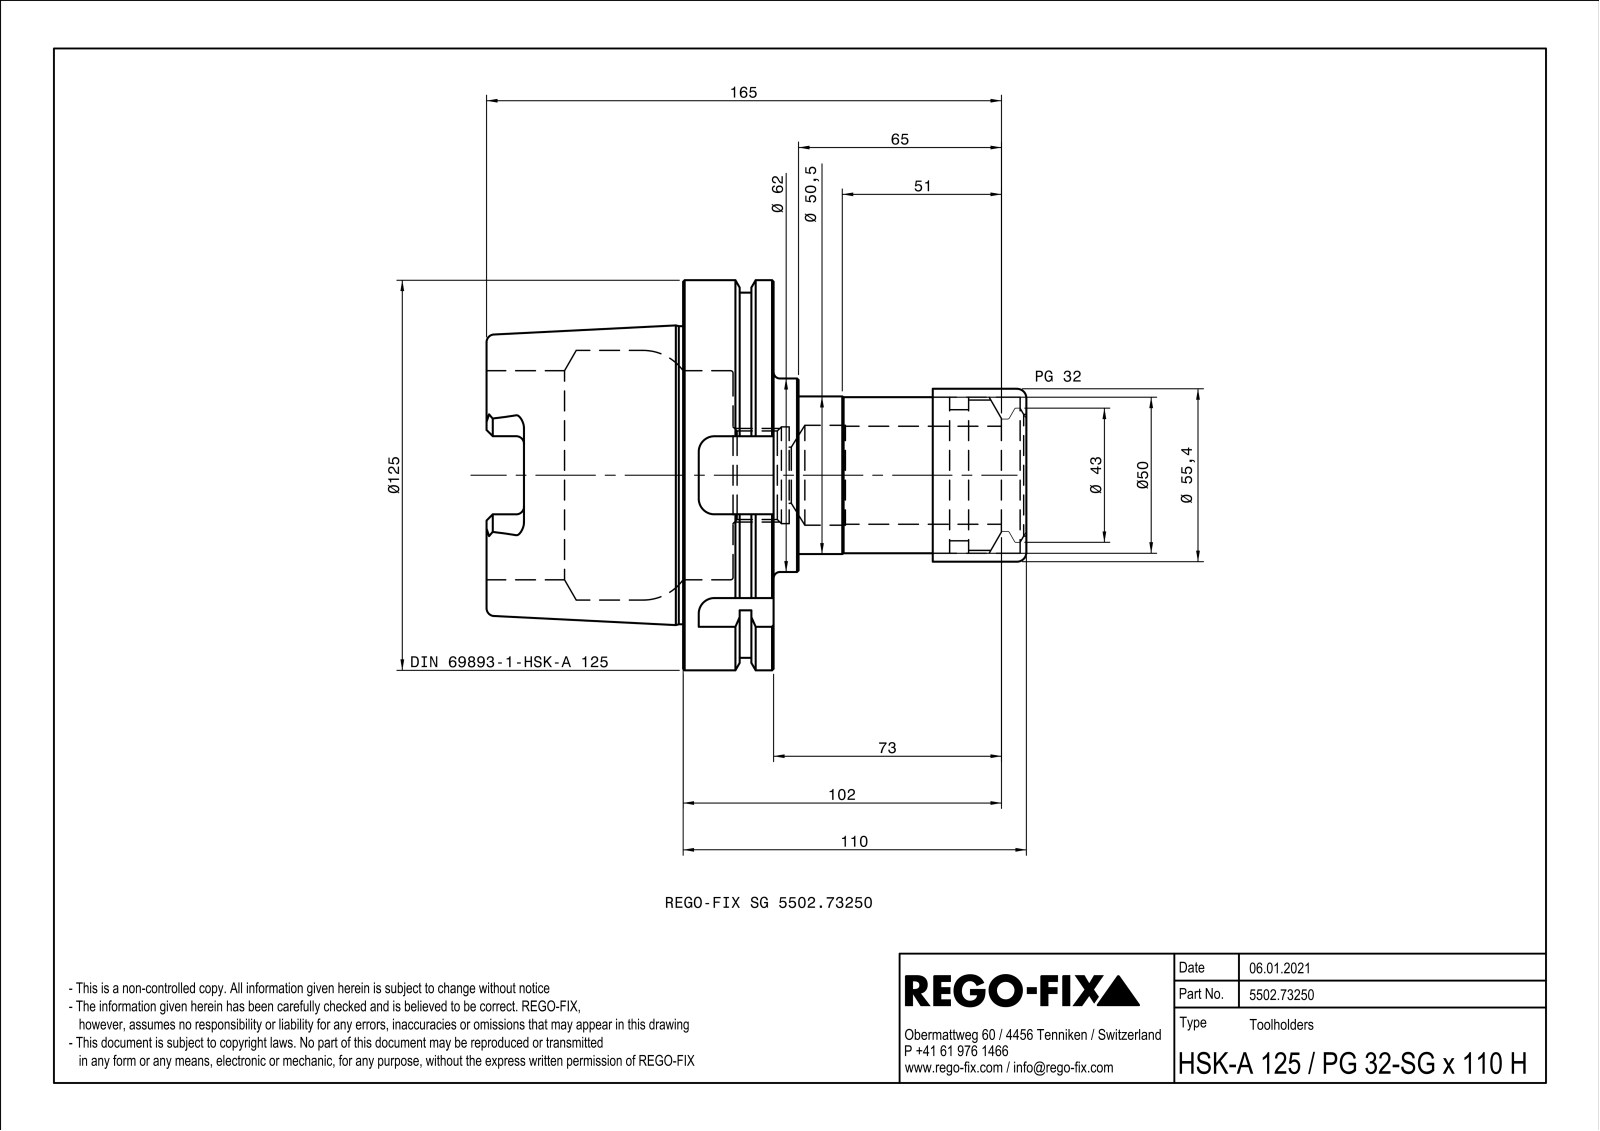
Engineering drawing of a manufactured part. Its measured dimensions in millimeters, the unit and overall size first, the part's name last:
Units: millimetres
Overall size (bounding box): 173 × 125 × 125
Round holes (diameter × count): ⌀10 ×1, ⌀18 ×1, ⌀28.38 ×1, ⌀31 ×1, ⌀33 ×1, ⌀38.25 ×1, ⌀48.38 ×1, ⌀50.05 ×1, ⌀51 ×1, ⌀67 ×1, ⌀80 ×1
Round bosses / shafts (diameter × count): ⌀125 ×1, ⌀117 ×1, ⌀95.51 ×1, ⌀62 ×1, ⌀55 ×1, ⌀50.5 ×1, ⌀50 ×1, ⌀42 ×1
Partial cylindrical surfaces — rounded edges, fillets, slot ends (radius × count): R2.5 ×6, R5 ×5, R5.88 ×4, R25.38 ×1, R27.12 ×1
Main face-to-face distances: 29, 13, 16, 79, 92, 63, 73, 81, 8, 94
Volume: 528 162 mm³ · Surface area: 104 792 mm²
Bodies: 2 solids, 155 faces (48 planar, 44 cylindrical, 63 other)
Part name (STEP PRODUCT): 0016242
STEP written by: SIEMENS PLM Software Solid Edge ST10 (AUTOMOTIVE_DESIGN)
